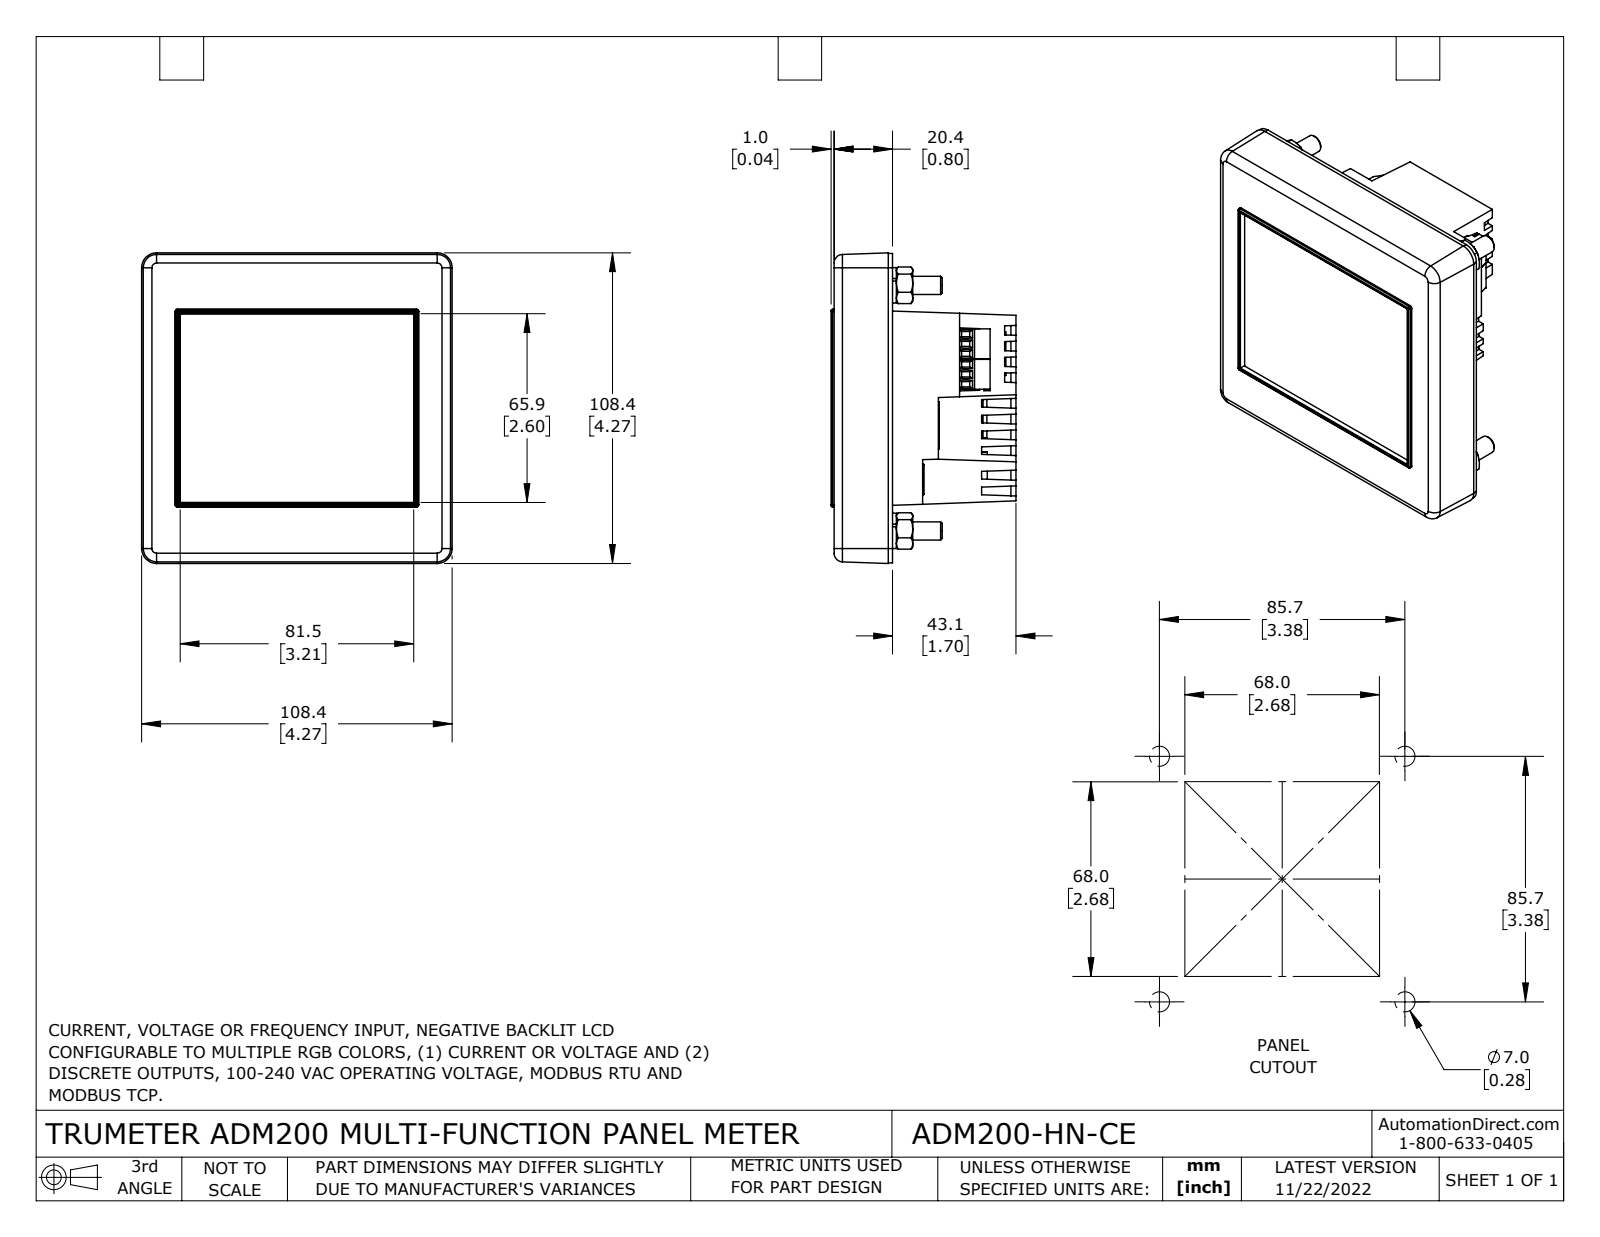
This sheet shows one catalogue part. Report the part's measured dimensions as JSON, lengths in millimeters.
{"part_name": "ADM200-HN-CE", "step_written_by": "SolidWorks 2021 (CONFIG_CONTROL_DESIGN)", "units": "millimeters", "bodies": {"solids": 23, "faces": 2059, "planar": 1384, "cylindrical": 290, "other": 385}, "overall_size": [108.4, 108.4, 64.5], "volume_mm3": 128000, "surface_area_mm2": 123100, "round_holes": [[1.8, 9], [2.9, 6], [3, 5], [5.4, 4], [6.4, 4], [6.6, 4], [7.5, 4], [3.9, 2]], "round_bosses_or_shafts": [[1, 5], [12.4, 4], [11.1, 4], [0.6, 4], [2, 2]], "partial_cylinders_radius": [[0.2, 32], [0.5, 30], [1, 7], [0.4, 4], [0.8, 4], [3, 4], [5, 4], [0.1, 2]], "face_to_face_distances": [0.8, 16.1, 2.8, 1.9, 1.5, 2, 17.6, 86.2, 88.1, 1.2], "hole_center_spacings": [18, 82, 3.5, 7.4, 25, 36, 54, 60.9]}
